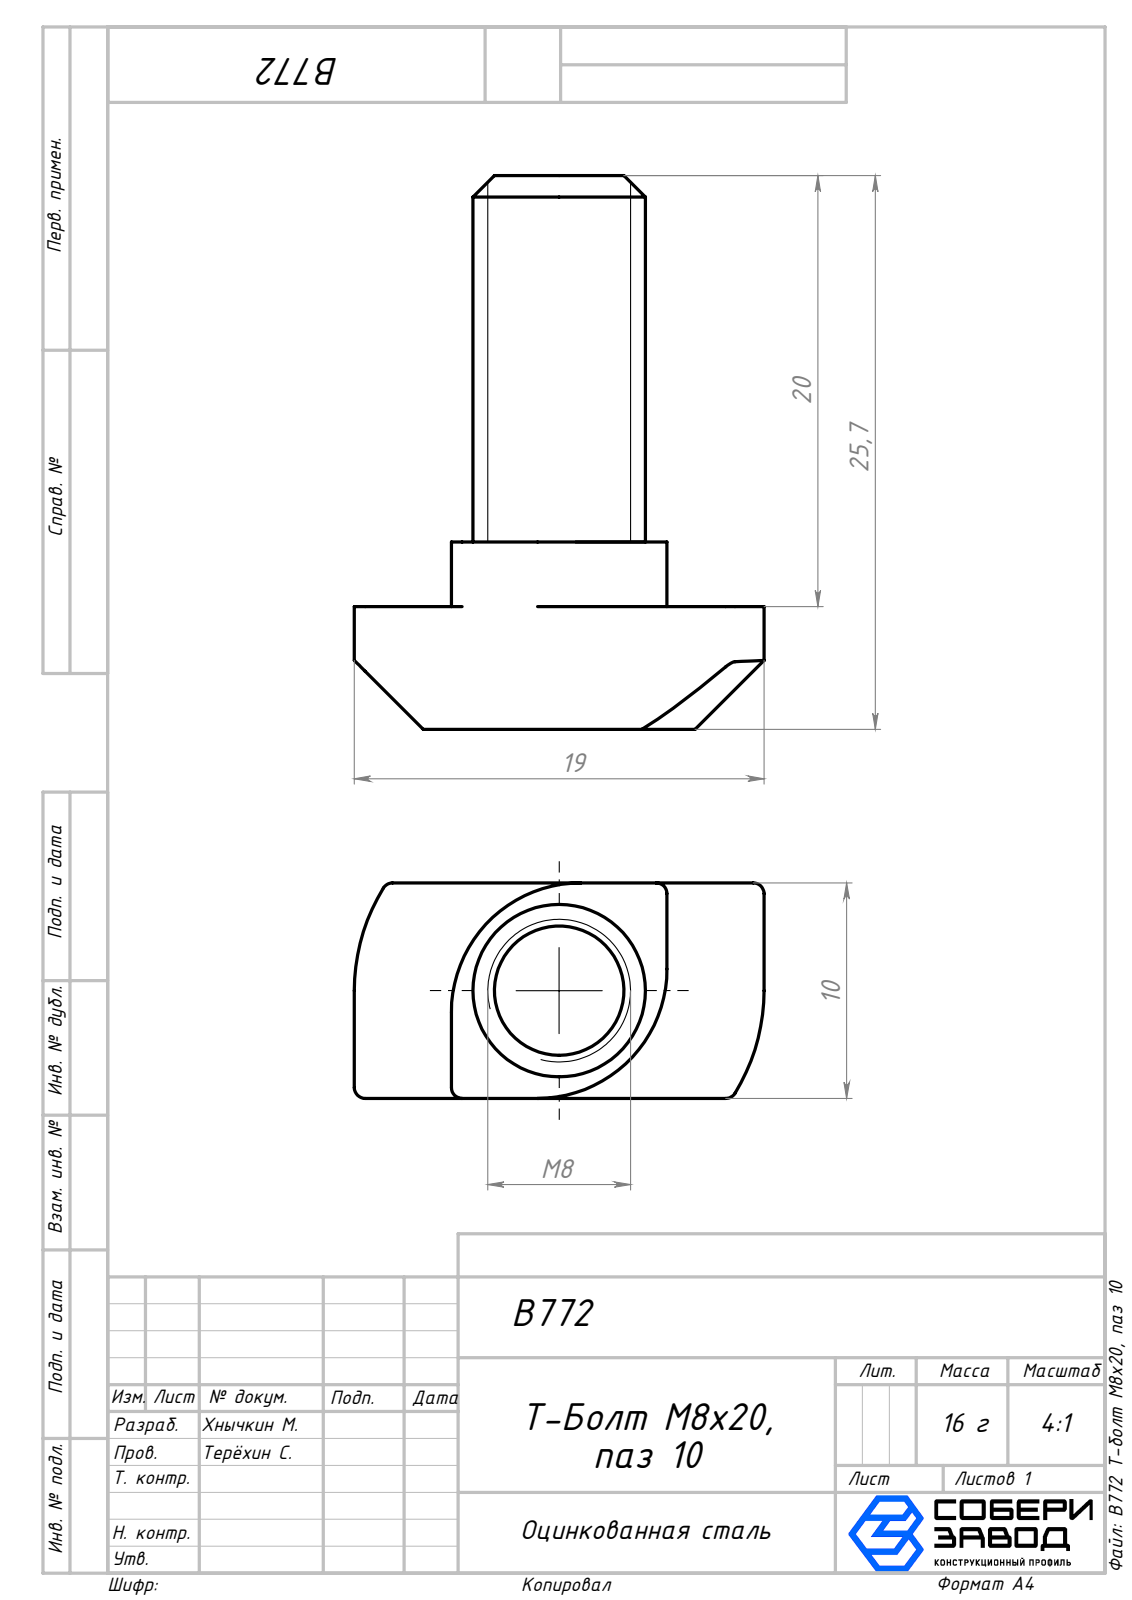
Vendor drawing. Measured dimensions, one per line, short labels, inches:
name: B772 Т-болт М8х20, паз 10
written by: SolidWorks 2025 (AUTOMOTIVE_DESIGN)
unit: in
bodies: 1 solid, 29 faces (13 planar, 12 cylindrical, 4 other)
size: 1.012 × 0.748 × 0.394
volume: 0.125 in³; area: 1.765 in²
bosses: 1× ⌀0.315
rounds: 6× R0.02, 2× R0.236, 2× R0.357
face distances: 0.394, 0.224, 0.343, 0.118, 1.012, 0.787, 0.669, 0.177, 0.571, 0.748
